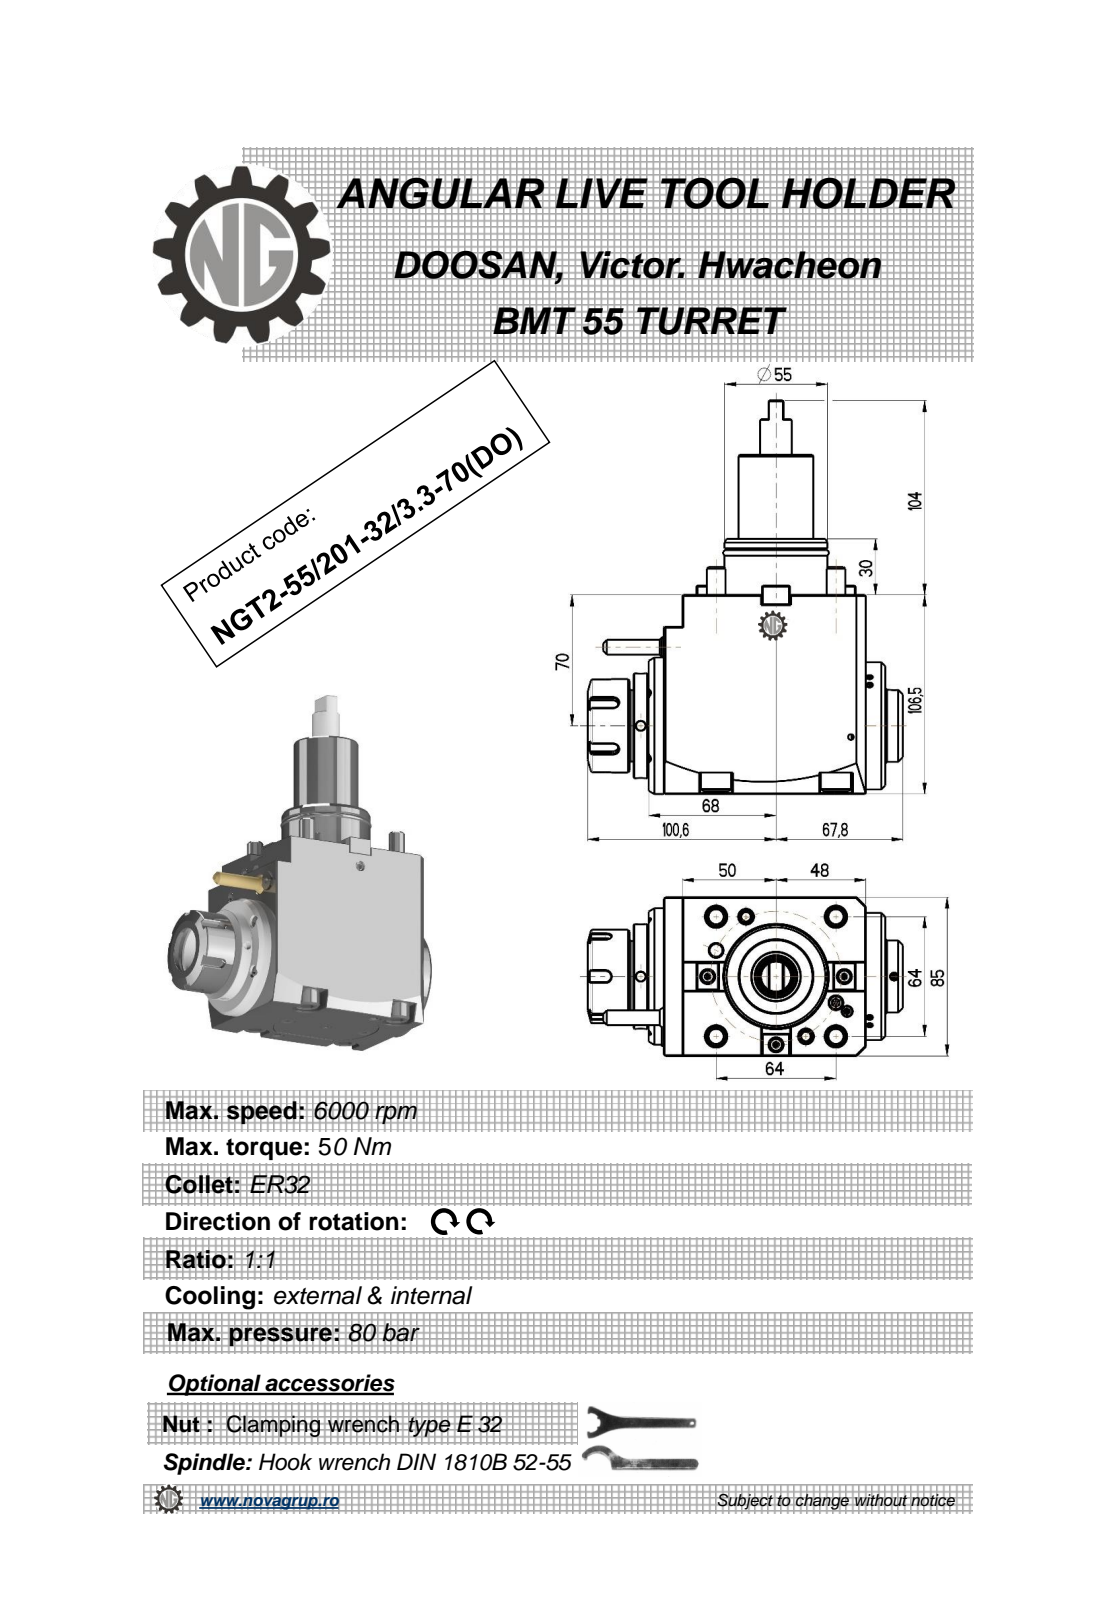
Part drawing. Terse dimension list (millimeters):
name: NGT2_55_201_32_3_3_70_DO
written by: PRO/ENGINEER BY PARAMETRIC TECHNOLOGY CORPORATION, 2010280 (CONFIG_CONTROL_DESIGN)
unit: mm
bodies: 2 solids, 479 faces (229 planar, 113 cylindrical, 137 other)
size: 210.5 × 168.4 × 85
volume: 1 221 000 mm³; area: 107 880 mm²
holes: 3× ⌀5, 2× ⌀6.8, 1× ⌀3, 1× ⌀12, 1× ⌀27
bosses: 4× ⌀16, 4× ⌀10, 2× ⌀50, 1× ⌀73, 1× ⌀68, 1× ⌀56, 1× ⌀55, 1× ⌀43.4
rounds: 20× R0.32, 6× R0.22, 5× R3, 4× R8.5, 2× R0.8, 2× R480
face distances: 85, 106.5, 8, 108, 116, 10, 18, 126.3, 118.3, 10.3
hole spacings: 42.62, 47.41, 69.86, 105.19
